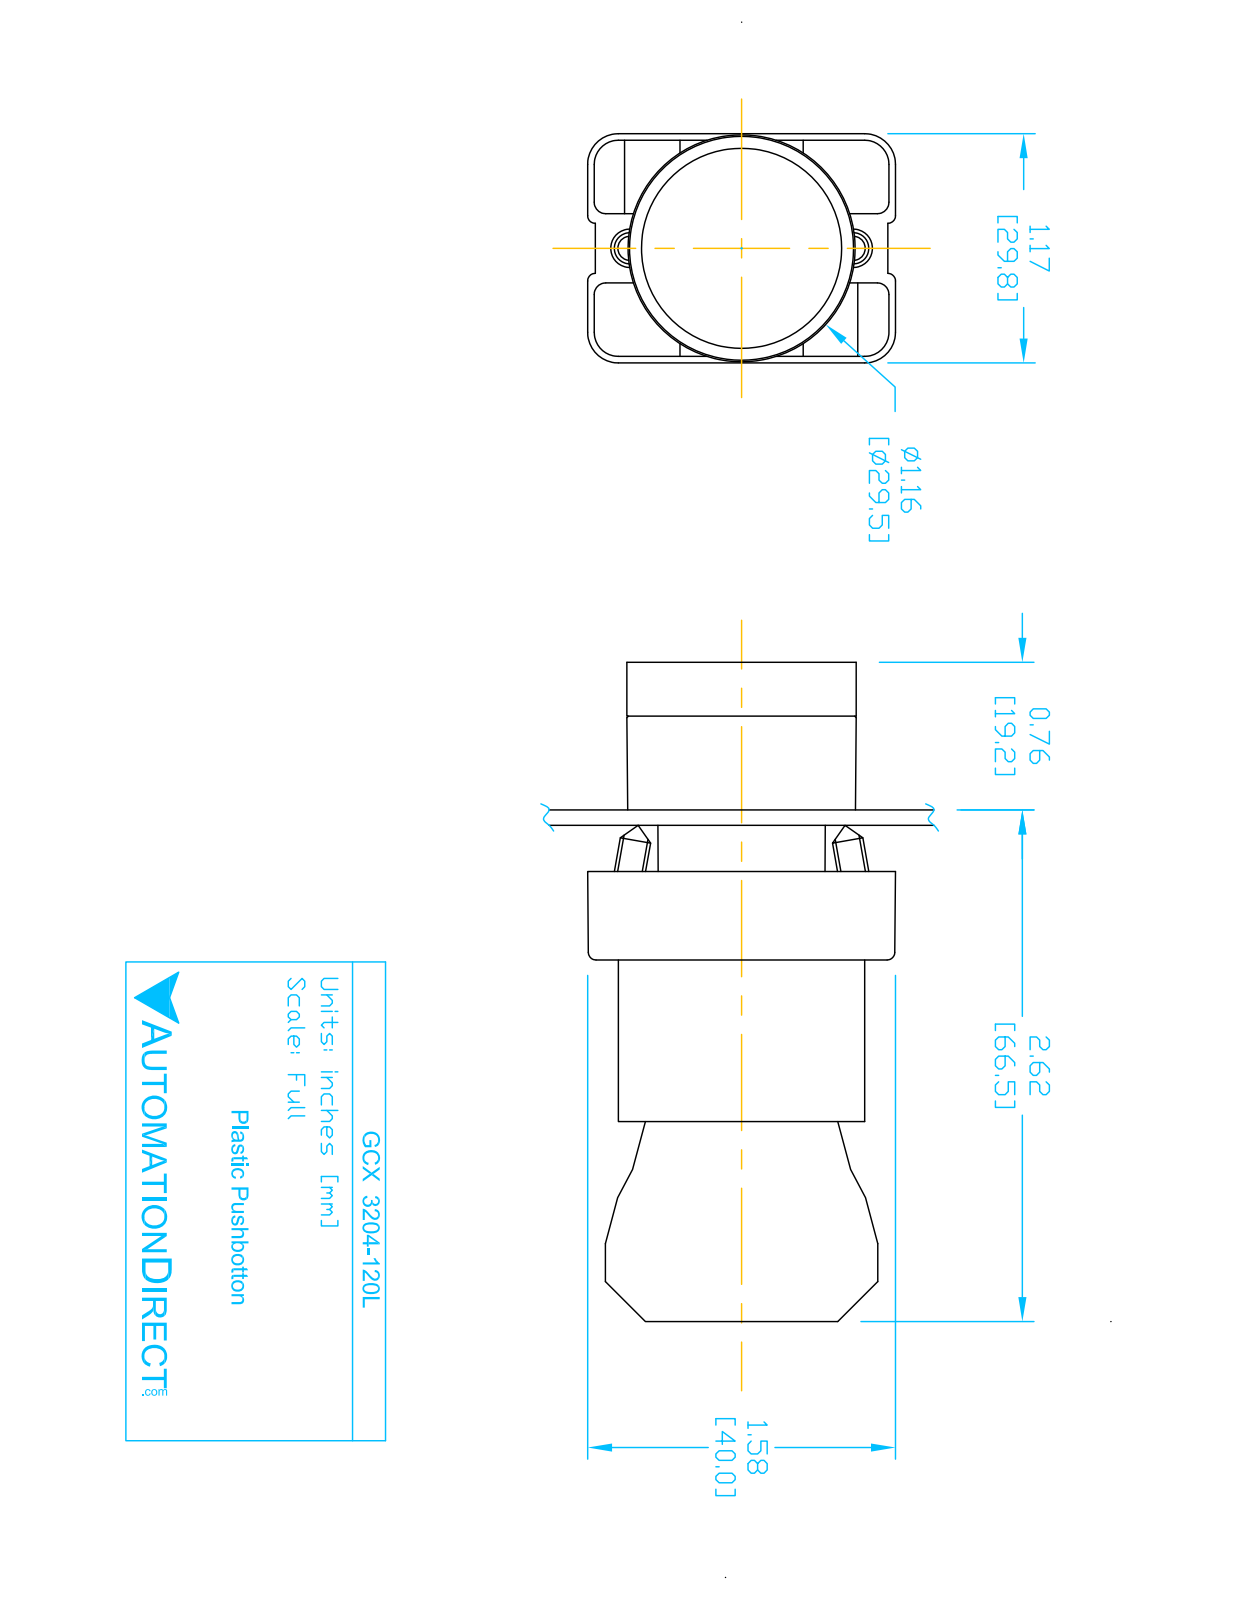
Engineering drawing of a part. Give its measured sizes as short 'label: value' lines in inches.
name: GCX3204-120L; GCX3204L OPERATOR; ecx1040; ECX1050 (+1 more)
written by: SolidWorks 2016 (AUTOMOTIVE_DESIGN)
unit: in
bodies: 8 solids, 431 faces (252 planar, 148 cylindrical, 31 other)
size: 3.319 × 1.581 × 1.177
volume: 2.794 in³; area: 38.77 in²
holes: 2× ⌀0.079, 2× ⌀0.124, 2× ⌀0.13, 1× ⌀0.087, 1× ⌀0.197, 1× ⌀0.469, 1× ⌀0.878, 1× ⌀0.888, 1× ⌀1.024
bosses: 4× ⌀0.157, 1× ⌀1.175, 1× ⌀1.004, 1× ⌀0.945, 1× ⌀0.856, 1× ⌀0.78, 1× ⌀0.504
rounds: 24× R0.059, 12× R0.041, 12× R0.124, 12× R0.157, 8× R0.039, 2× R0.128, 1× R0.02, 1× R0.063
face distances: 0.827, 0.579, 2.02, 1.193, 1.171, 0.276, 2.295, 1.469, 0.031, 0.033
hole spacings: 0.236, 0.544, 0.472, 0.49
